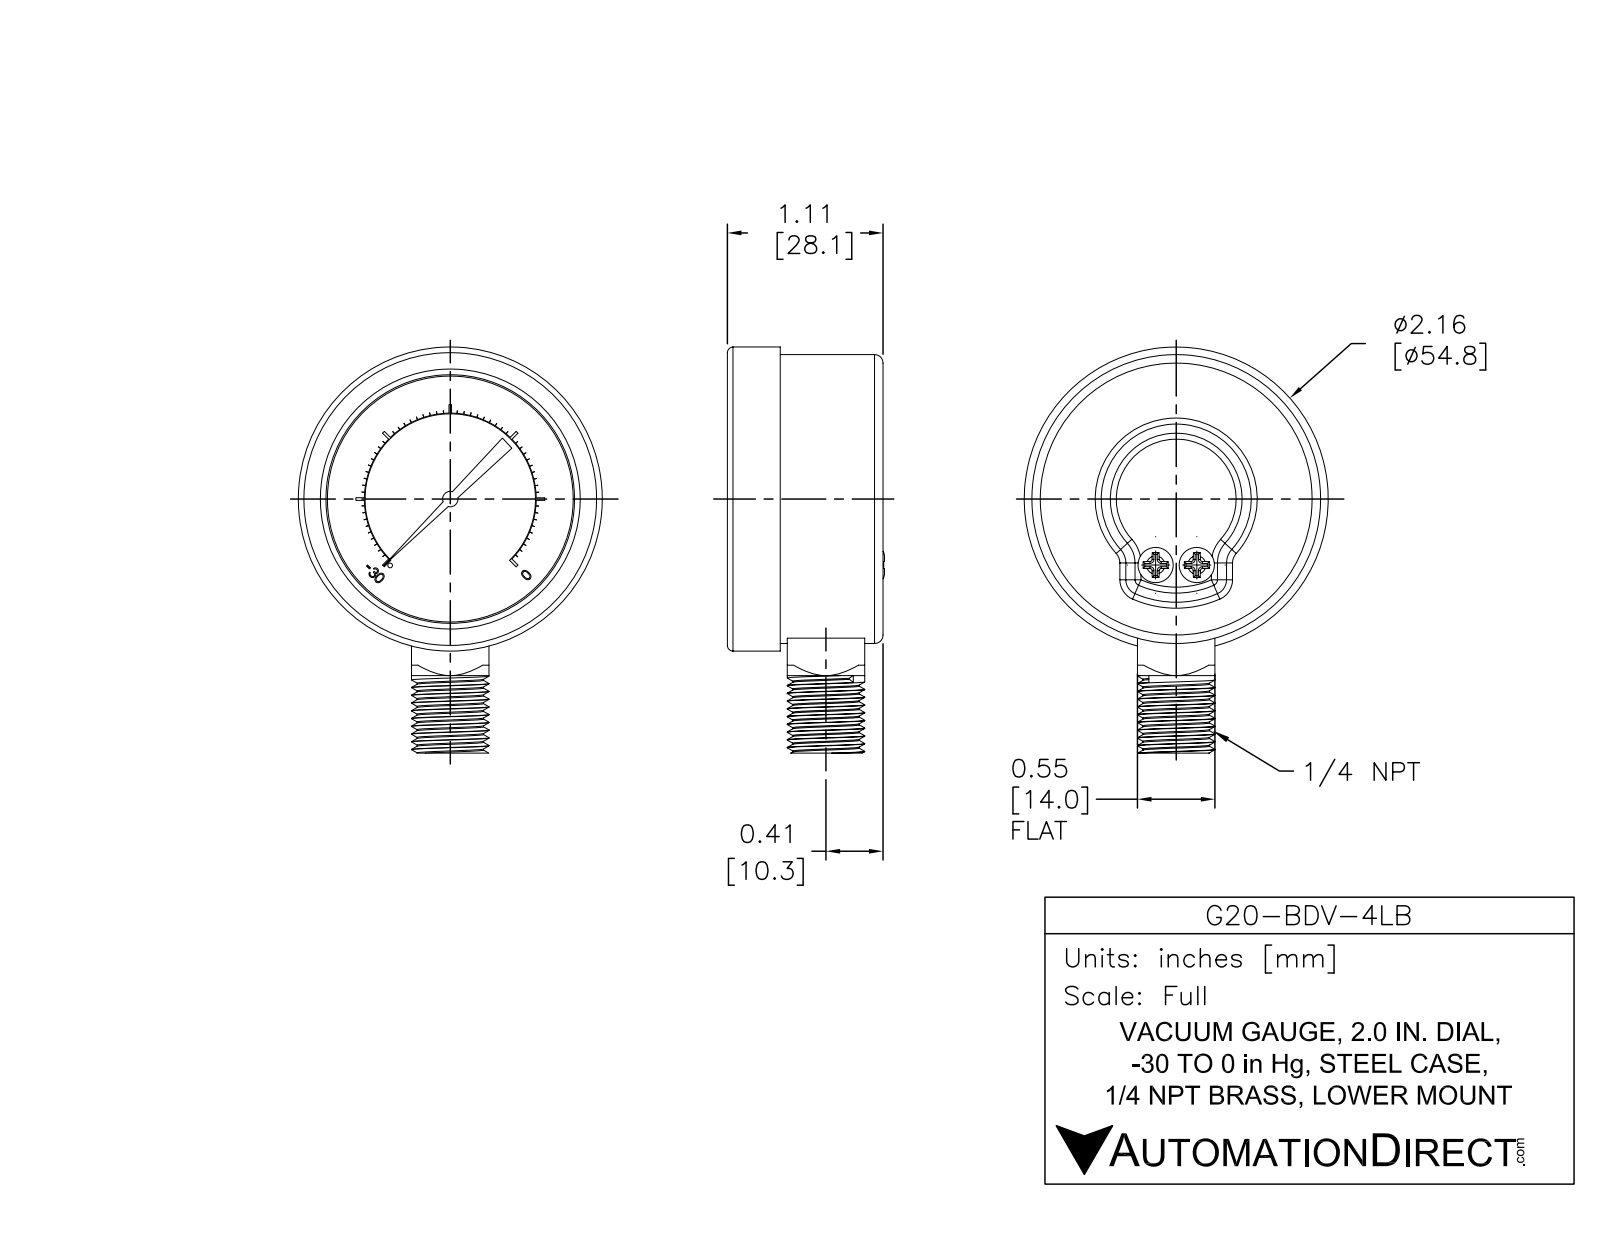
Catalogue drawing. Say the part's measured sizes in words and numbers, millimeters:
The part is named "G20-BDV-4LB". Its 3-D file was written by "SolidWorks 2021 (AUTOMOTIVE_DESIGN)". It is 1 solid with 425 faces: 274 planar, 81 cylindrical and 70 other. Overall it measures 73.2 by 54.8 by 28.3 millimeters. Its volume is 52 140 cubic millimeters and its surface area 11 630 square millimeters. Round holes: 1 of diameter 3.6, 1 of diameter 44.3. Round bosses or shafts: 2 of diameter 6.4, 1 of diameter 54.8, 1 of diameter 52.1, 1 of diameter 14, 1 of diameter 2.8, 1 of diameter 0.8. Partial cylindrical surfaces (rounded edges, fillets, slot ends): 4 of radius 1.5, 1 of radius 15.4, 1 of radius 15.5. The main face-to-face distances are 20.7, 28.1, 7.4, 2.5, 18.2, 25.5, 16, 18.5, 2.2, 9.5.
